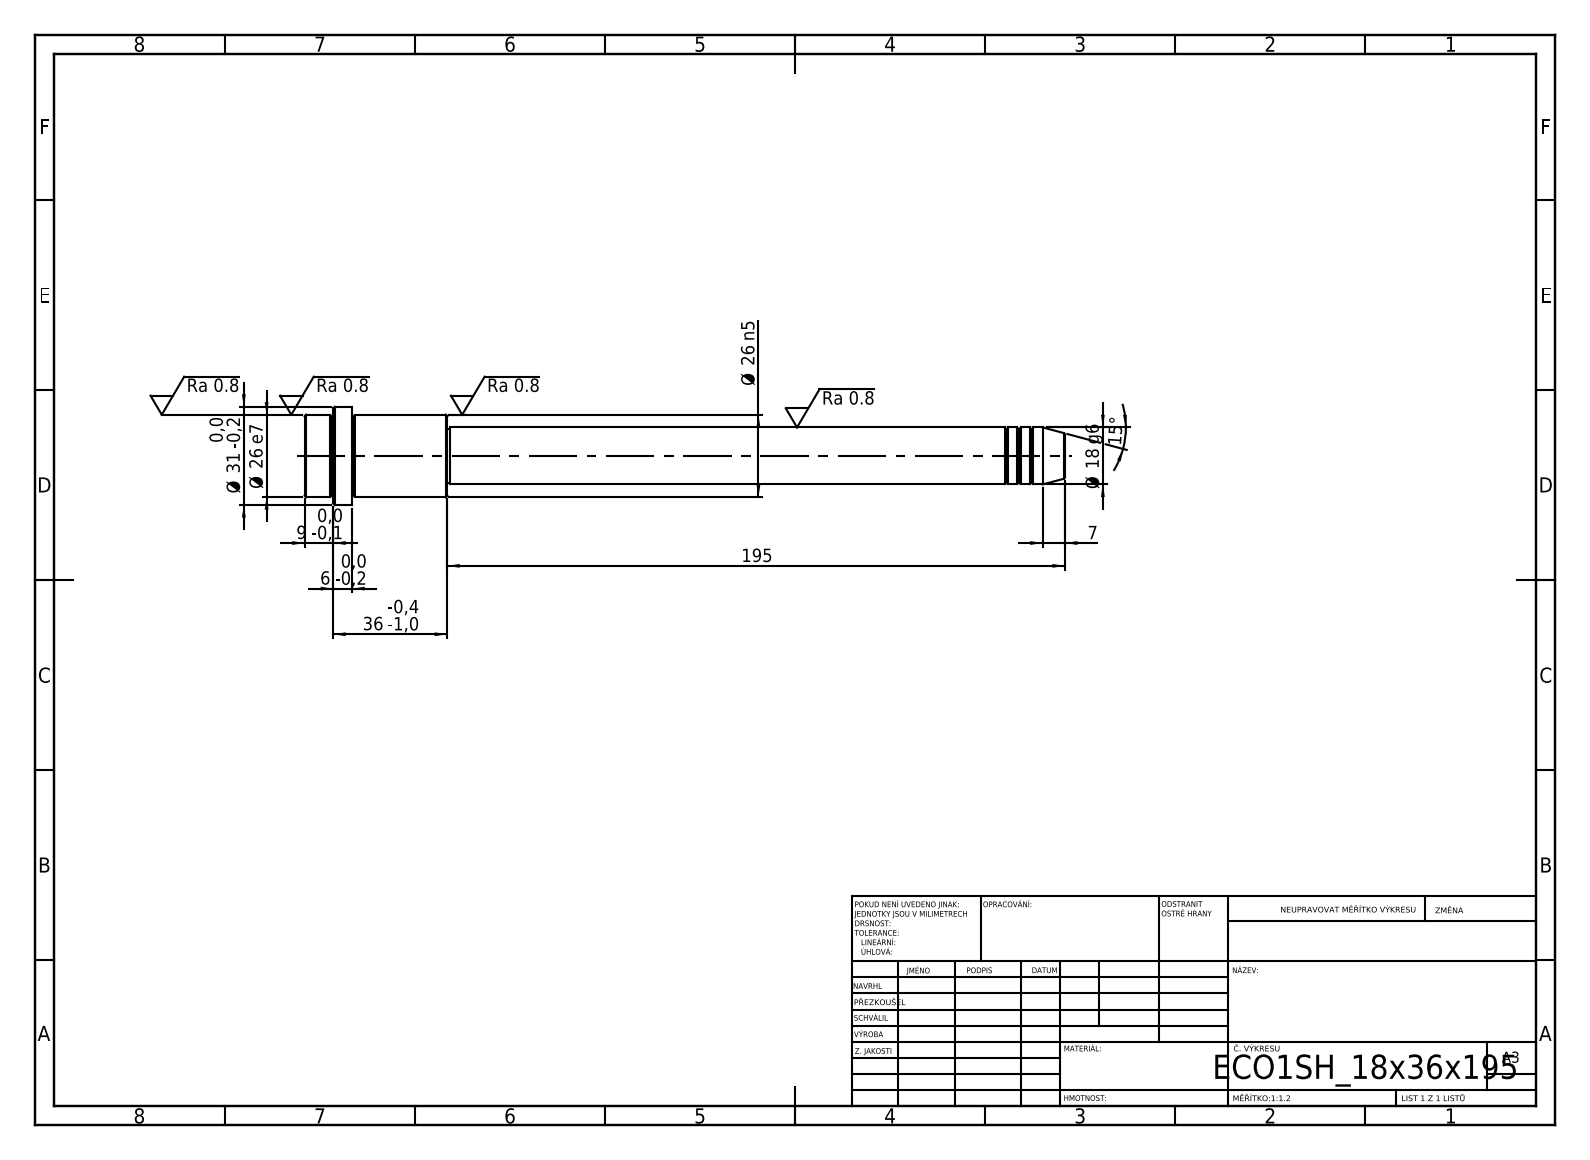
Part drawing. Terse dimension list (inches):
written by: SolidWorks 2019 (CONFIG_CONTROL_DESIGN)
unit: in
bodies: 1 solid, 52 faces (6 planar, 16 cylindrical, 30 other)
size: 9.449 × 1.22 × 1.22
volume: 4.535 in³; area: 25.31 in²
bosses: 1× ⌀1.22, 1× ⌀1.024, 1× ⌀0.709, 1× ⌀0.669
face distances: 1.772, 1.181, 0.591, 1.417, 0.236, 0.354, 7.677, 8.858, 9.094, 9.449
